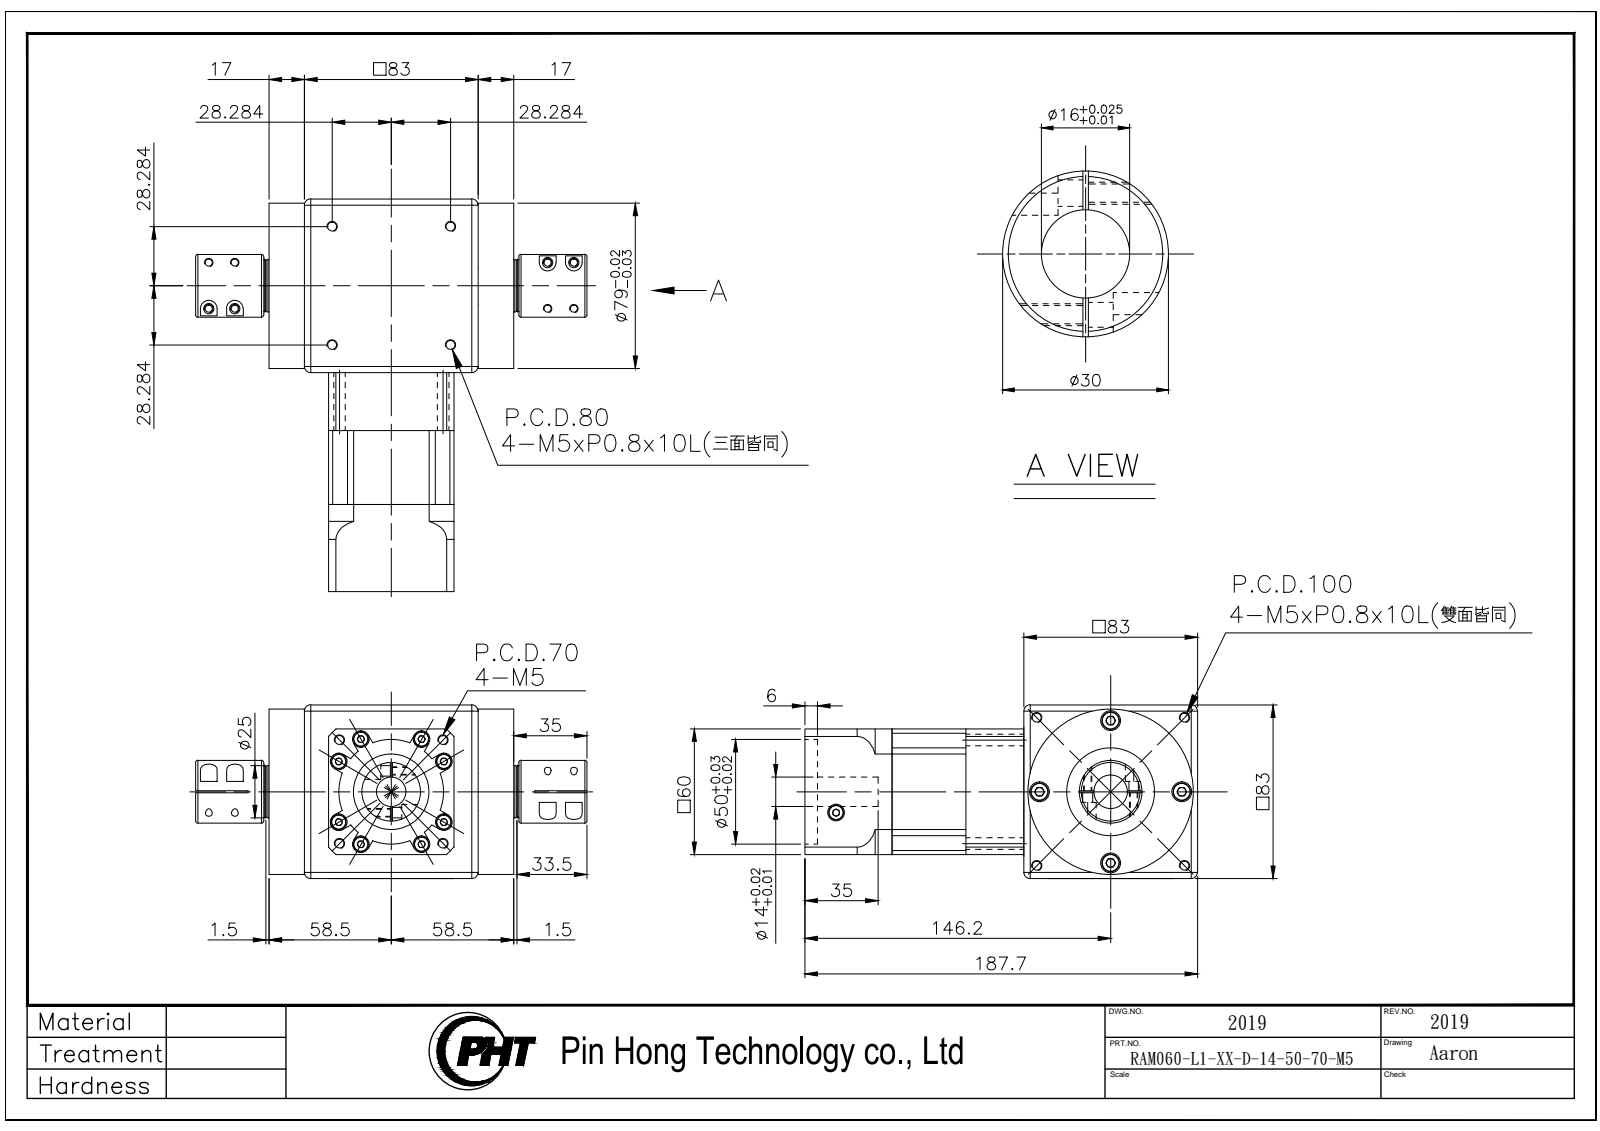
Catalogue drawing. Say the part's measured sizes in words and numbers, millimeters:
The part is named "RAM060-L1-XX-D-14-50-70-M5_2019". Its 3-D file was written by "SolidWorks 2016 (AUTOMOTIVE_DESIGN)". It is 4 solids with 1100 faces: 539 planar, 365 cylindrical and 196 other. Overall it measures 187.7 by 187 by 83 millimeters. Its volume is 1 055 000 cubic millimeters and its surface area 143 278 square millimeters. Round holes: 16 of diameter 4.2, 10 of diameter 8, 8 of diameter 4.1, 8 of diameter 4.5, 8 of diameter 4.8, 8 of diameter 5.5, 4 of diameter 9.5, 1 of diameter 14, 1 of diameter 16, 1 of diameter 16.6, 1 of diameter 36. Round bosses or shafts: 16 of diameter 7, 8 of diameter 8.5, 8 of diameter 7.6, 8 of diameter 4, 1 of diameter 79, 1 of diameter 55, 1 of diameter 42, 1 of diameter 30. Partial cylindrical surfaces (rounded edges, fillets, slot ends): 8 of radius 4, 4 of radius 5, 1 of radius 25, 1 of radius 35, 1 of radius 40, 1 of radius 57.15. The main face-to-face distances are 83, 11.5, 71.5, 60, 28.5, 27.7, 35.35, 63.05, 88.5, 146.05. The hole center spacings are 29, 10.26, 14.14, 39.25, 41.01, 42.9, 50.9, 53.15.
